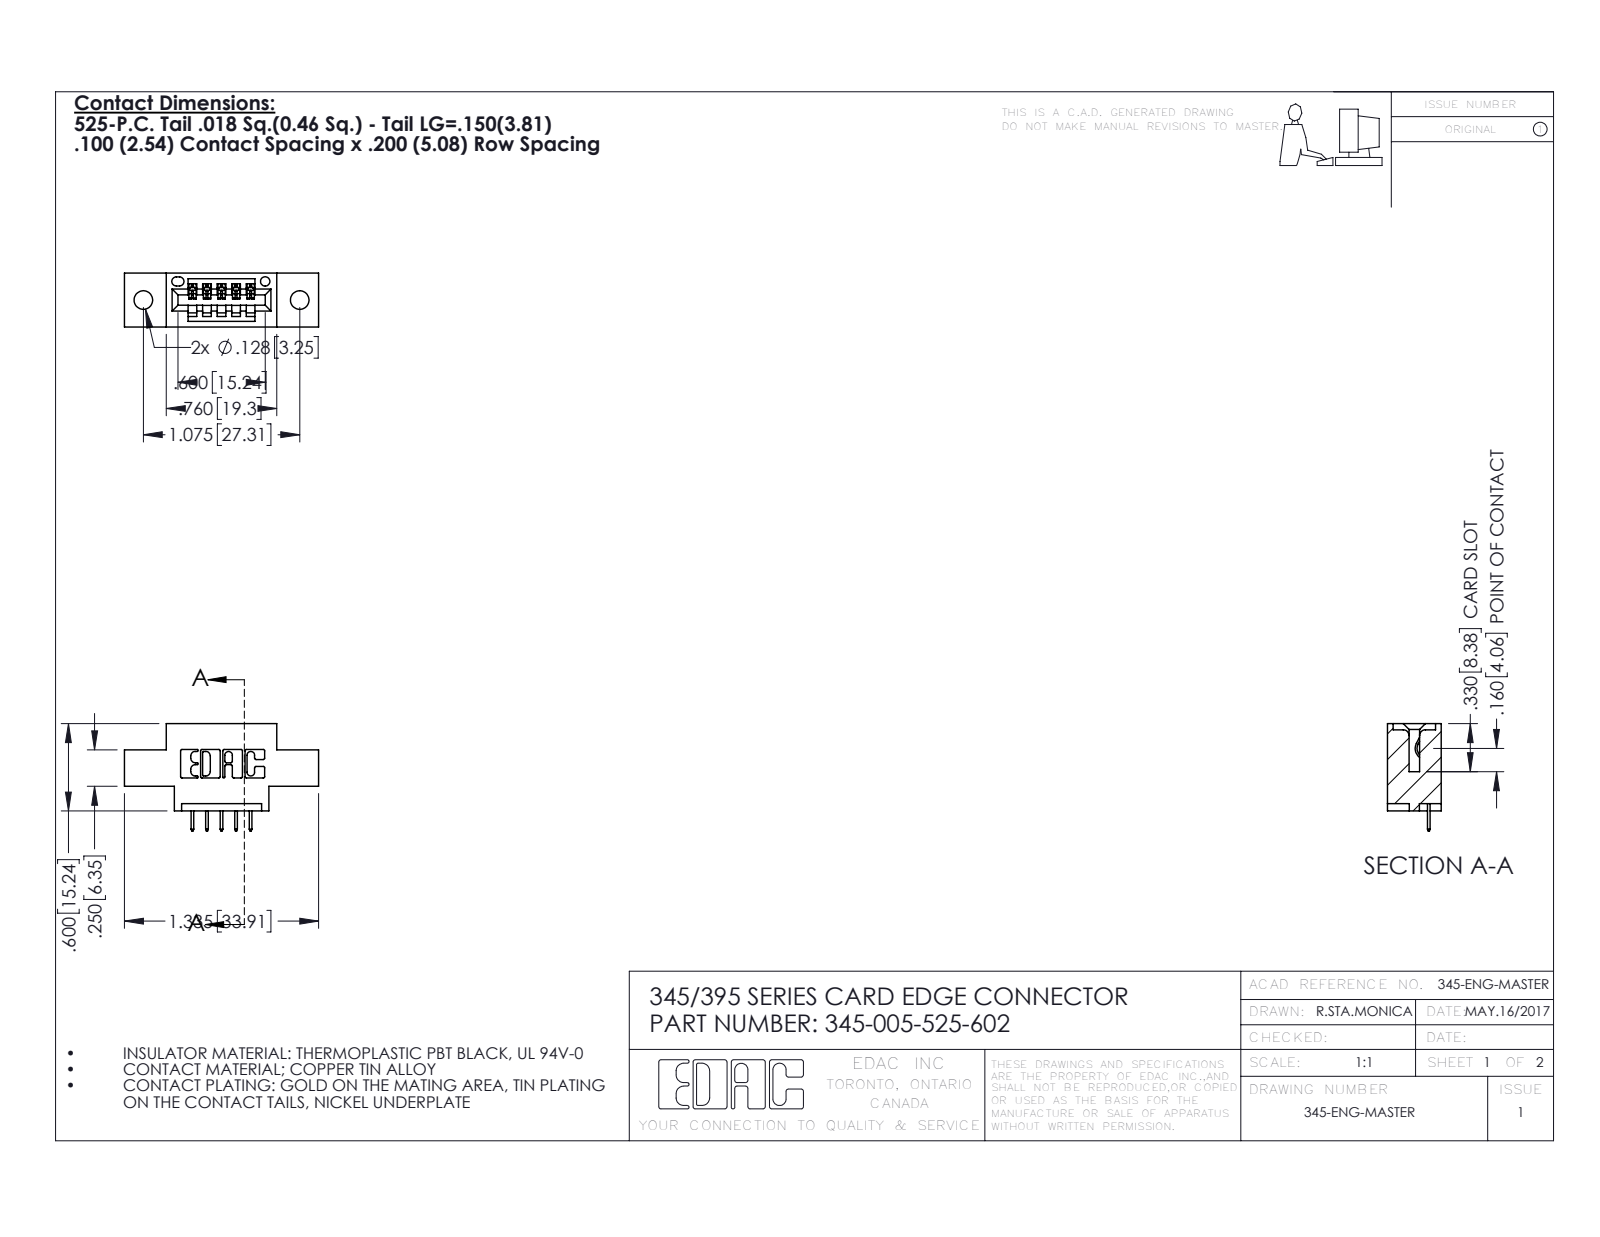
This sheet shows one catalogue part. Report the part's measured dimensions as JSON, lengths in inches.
{"part_name": "345 Part_0.170 Offset - 0.128 Dia; 345-292-001_345-293-125; 345-005-525-602", "step_written_by": "SolidWorks 2020 (CONFIG_CONTROL_DESIGN)", "units": "inches", "bodies": {"solids": 6, "faces": 440, "planar": 314, "cylindrical": 126, "other": 0}, "overall_size": [1.335, 0.737, 0.37], "volume_in3": 0.168, "surface_area_in2": 4.549, "round_holes": [[0.128, 2], [0.064, 1]], "partial_cylinders_radius": [[0.01, 22], [0.006, 10], [0.007, 6], [0.031, 6], [0.026, 3], [0.031, 2], [0.04, 2], [0.014, 1]], "face_to_face_distances": [0.37, 0.2, 0.1, 0.072, 0.298, 0.25, 0.025, 0.06, 0.55, 0.15], "hole_center_spacings": [0.27, 0.847, 1.075]}
